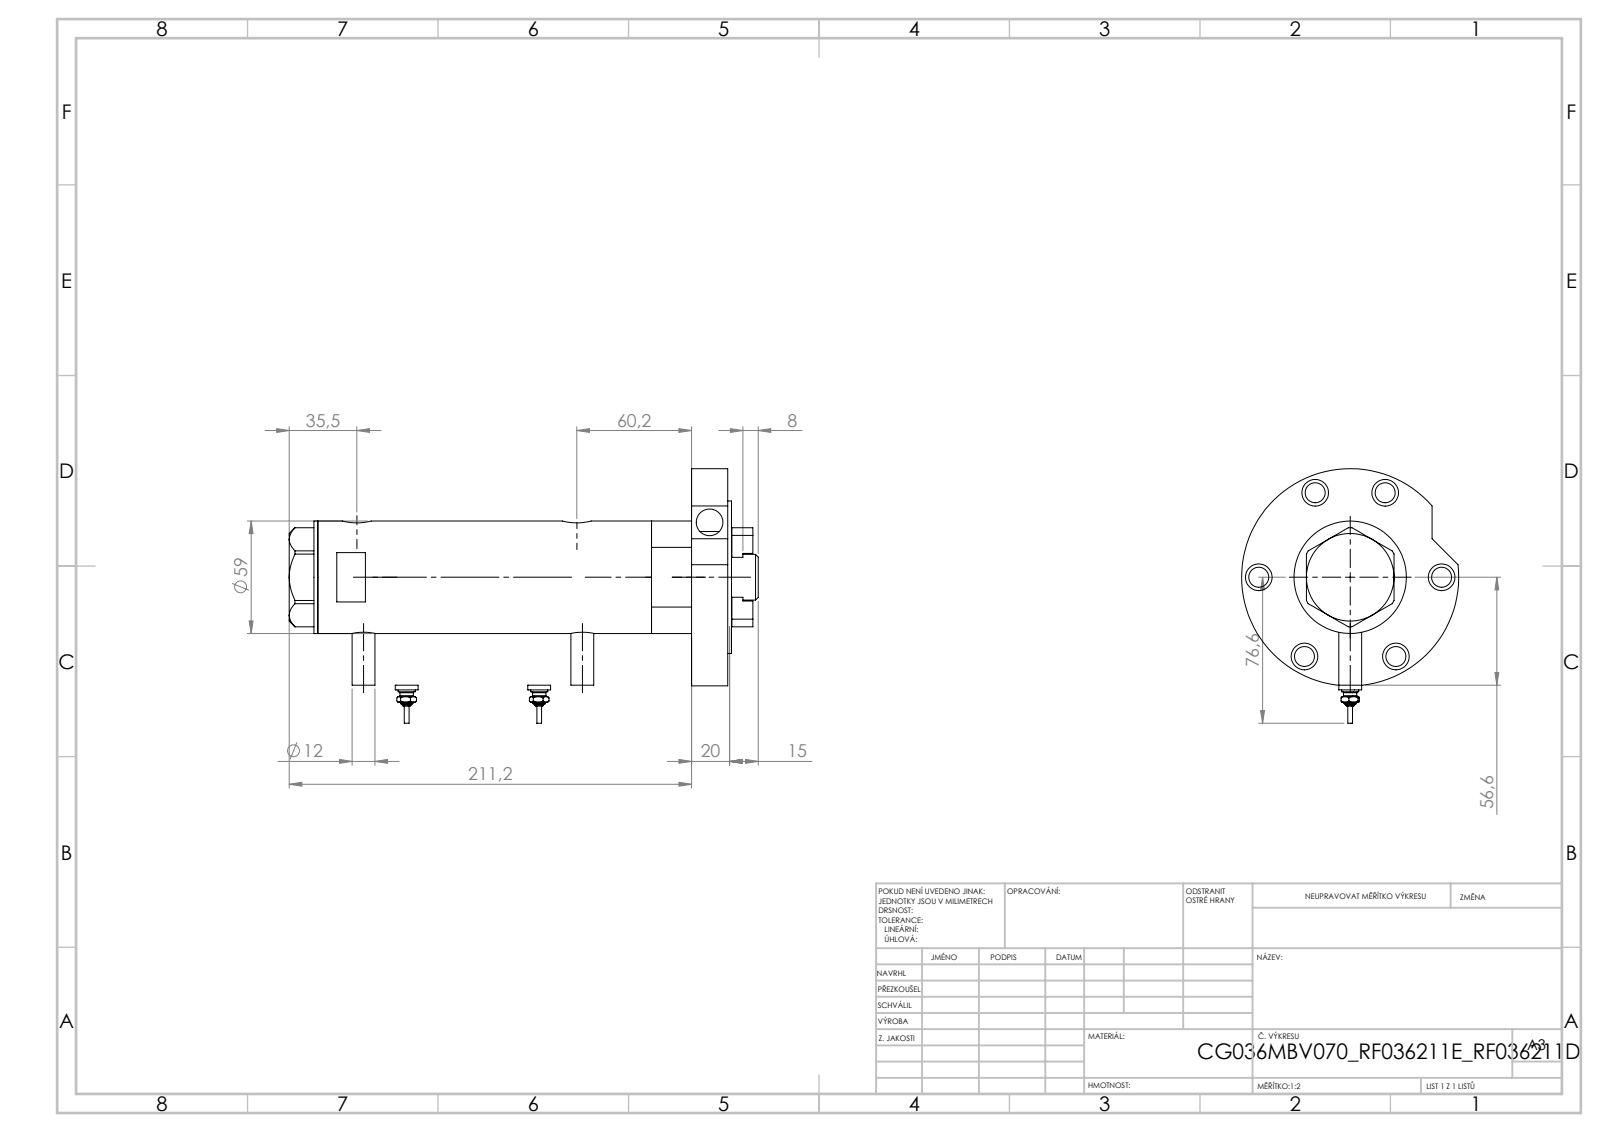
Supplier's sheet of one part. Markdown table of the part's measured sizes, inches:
| quantity | value |
| --- | --- |
| part name | V270CG_BACK; V270CG_VC; V270CG_RF211E; V270CG_FRONT (+3 more) |
| STEP written by | SolidWorks 2019 (CONFIG_CONTROL_DESIGN) |
| units | inches |
| bodies | 9 solids, 316 faces (116 planar, 126 cylindrical, 74 other) |
| overall size | 9.19 × 4.677 × 4.488 |
| volume | 40.88 in³ |
| surface area | 229.2 in² |
| round holes (diameter × count) | 0.413 × 10, 0.551 × 7, 0.24 × 4, 0.197 × 2, 0.383 × 2, 0.492 × 2, 0.591 × 2, 0.335 × 1, 0.984 × 1, 1.043 × 1, 1.417 × 1, 1.575 × 1 |
| round bosses / shafts (diameter × count) | 0.472 × 4, 0.354 × 2, 0.276 × 2, 0.171 × 2, 0.094 × 2, 4.488 × 1, 3.15 × 1, 2.323 × 1 |
| main face-to-face distances | 0.748, 0.079, 7.946, 0.827, 7.12, 7.868, 5.013, 2.106, 2.854, 2.933 |
| hole center spacings | 1.89, 0.784, 1.815, 2.254, 0.114, 0.138, 0.472, 1.111 |
